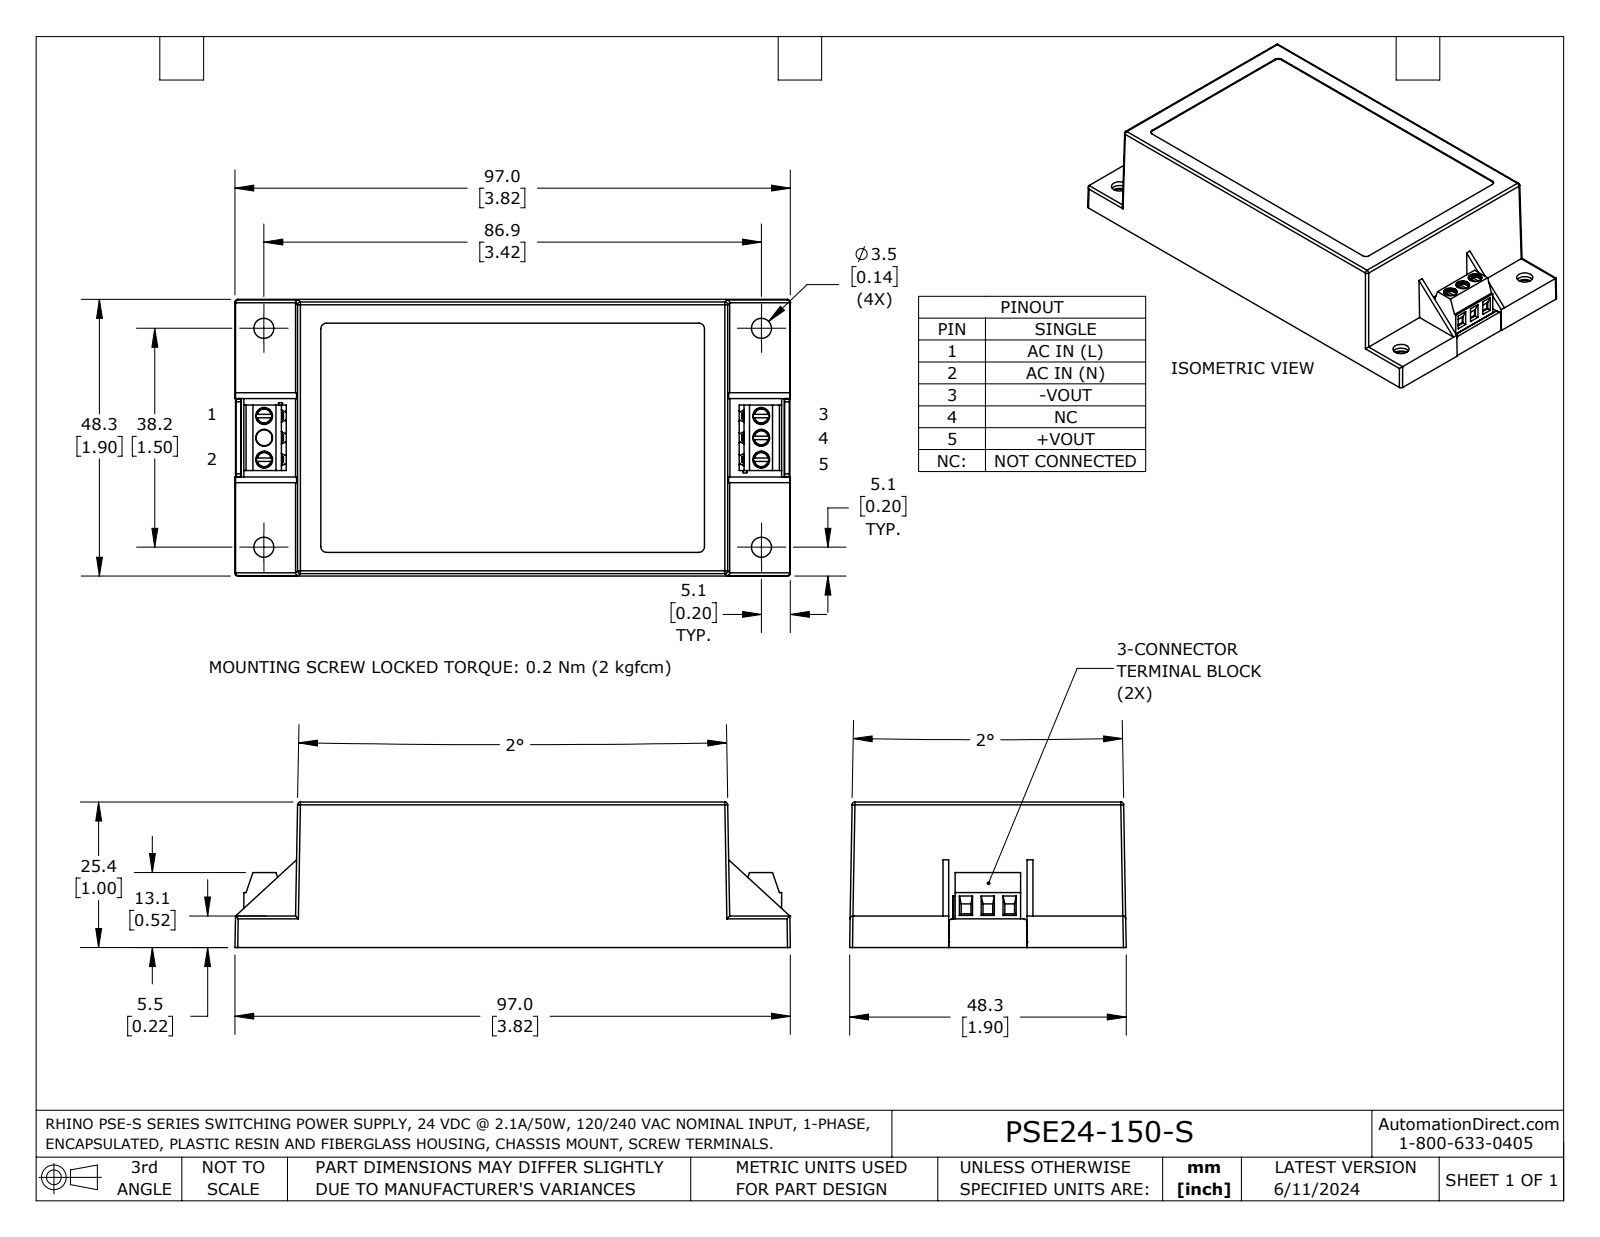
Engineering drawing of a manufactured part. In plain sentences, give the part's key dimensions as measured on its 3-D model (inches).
The part is named "PSE24-150-S". Its 3-D file was written by "SolidWorks 2023 (AUTOMOTIVE_DESIGN)". It is 5 solids with 560 faces: 396 planar, 130 cylindrical and 34 other. Overall it measures 3.819 by 1.902 by 1 inches. Its volume is 1.175 cubic inches and its surface area 63.85 square inches. Round holes: 6 of diameter 0.116, 4 of diameter 0.138, 4 of diameter 0.161, 1 of diameter 0.11. Partial cylindrical surfaces (rounded edges, fillets, slot ends): 18 of radius 0.009, 18 of radius 0.02, 12 of radius 0.006, 8 of radius 0.004, 4 of radius 0.008, 4 of radius 0.01, 4 of radius 0.039, 4 of radius 0.079. The main face-to-face distances are 0.039, 0.138, 0.815, 0.953, 0.177, 0.098, 0.776, 0.913, 0.854, 0.992. The hole center spacings are 0.15, 3.42, 3.417, 0.3, 0.602, 0.602, 0.752, 0.752.
